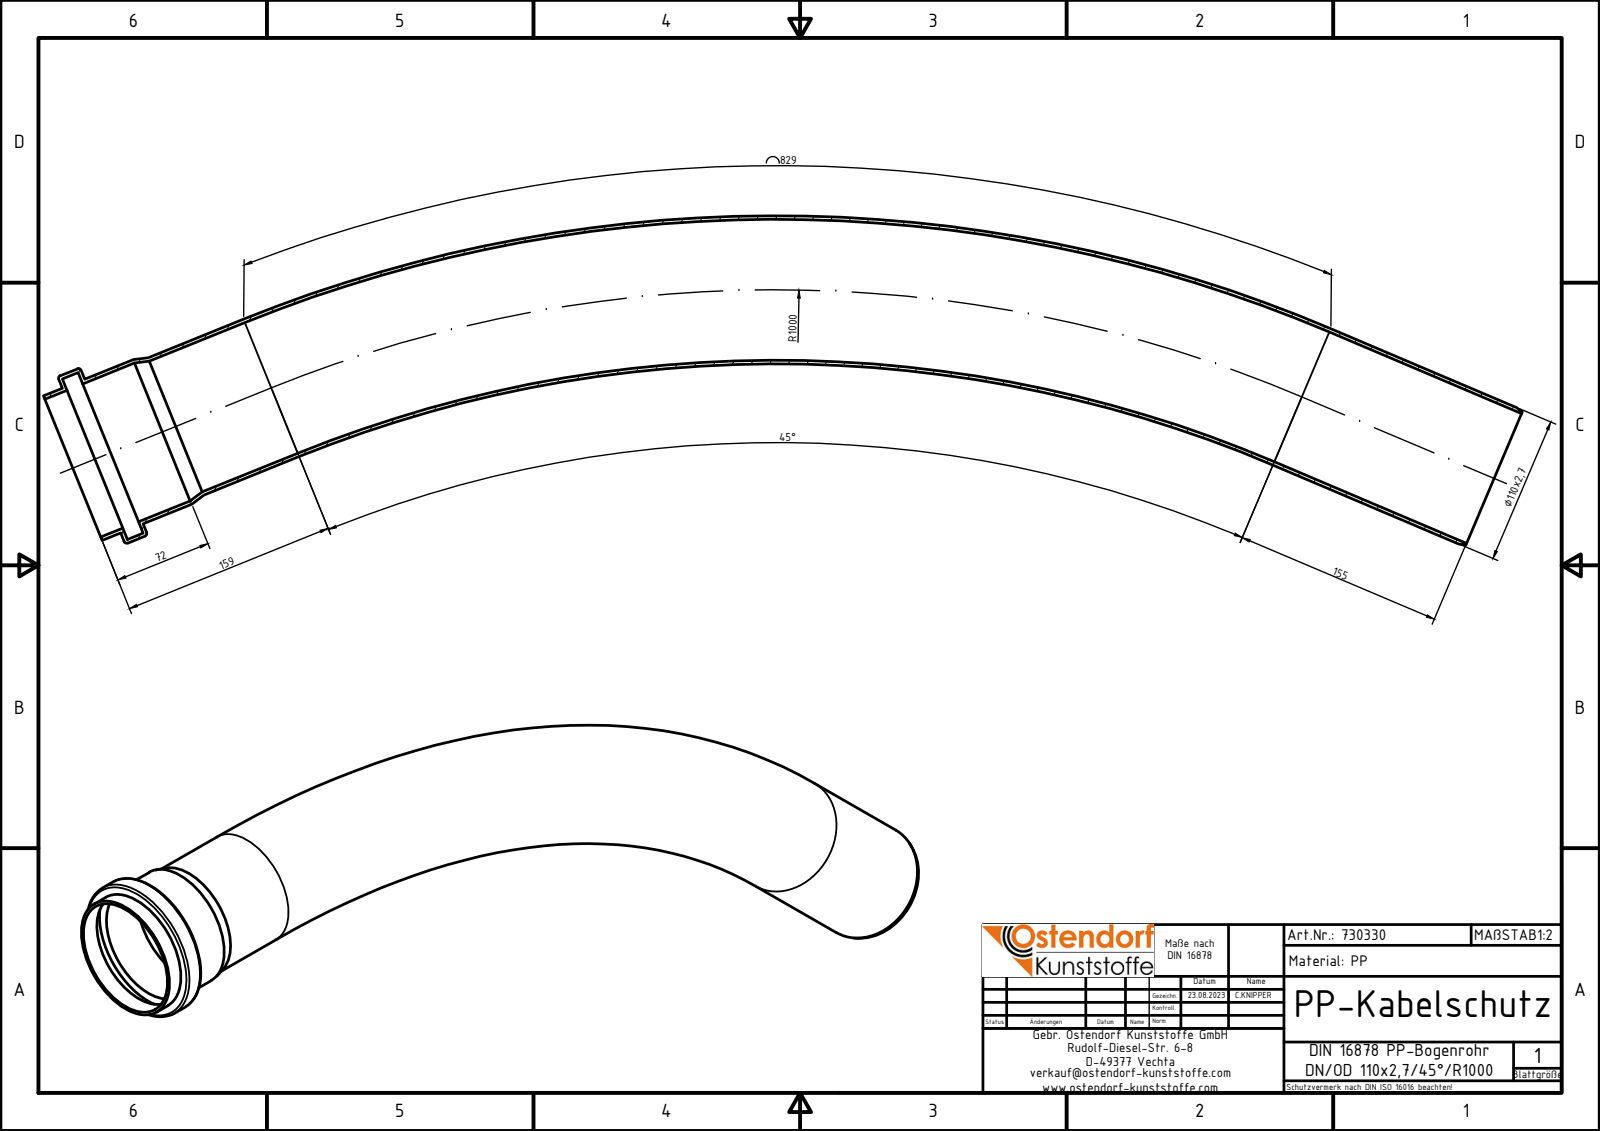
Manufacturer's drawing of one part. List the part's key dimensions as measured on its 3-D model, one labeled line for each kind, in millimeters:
Part name (STEP PRODUCT): PP-Bogenrohr_110x27_R1000_45_SM_34875_730330
STEP written by: Autodesk Inventor 2024 (AUTOMOTIVE_DESIGN)
Units: millimetres
Bodies: 1 solid, 23 faces (6 planar, 10 cylindrical, 7 other)
Overall size (bounding box): 1013.65 × 507.44 × 134
Volume: 1 024 000 mm³ · Surface area: 760 726 mm²
Round holes (diameter × count): ⌀104.6 ×2, ⌀110.4 ×1, ⌀128.6 ×1
Round bosses / shafts (diameter × count): ⌀110 ×2, ⌀134 ×1, ⌀115.8 ×1
Main face-to-face distances: 12.6, 15.31, 2.71, 2.69, 15.29, 18, 15, 17.69, 30.29, 33
